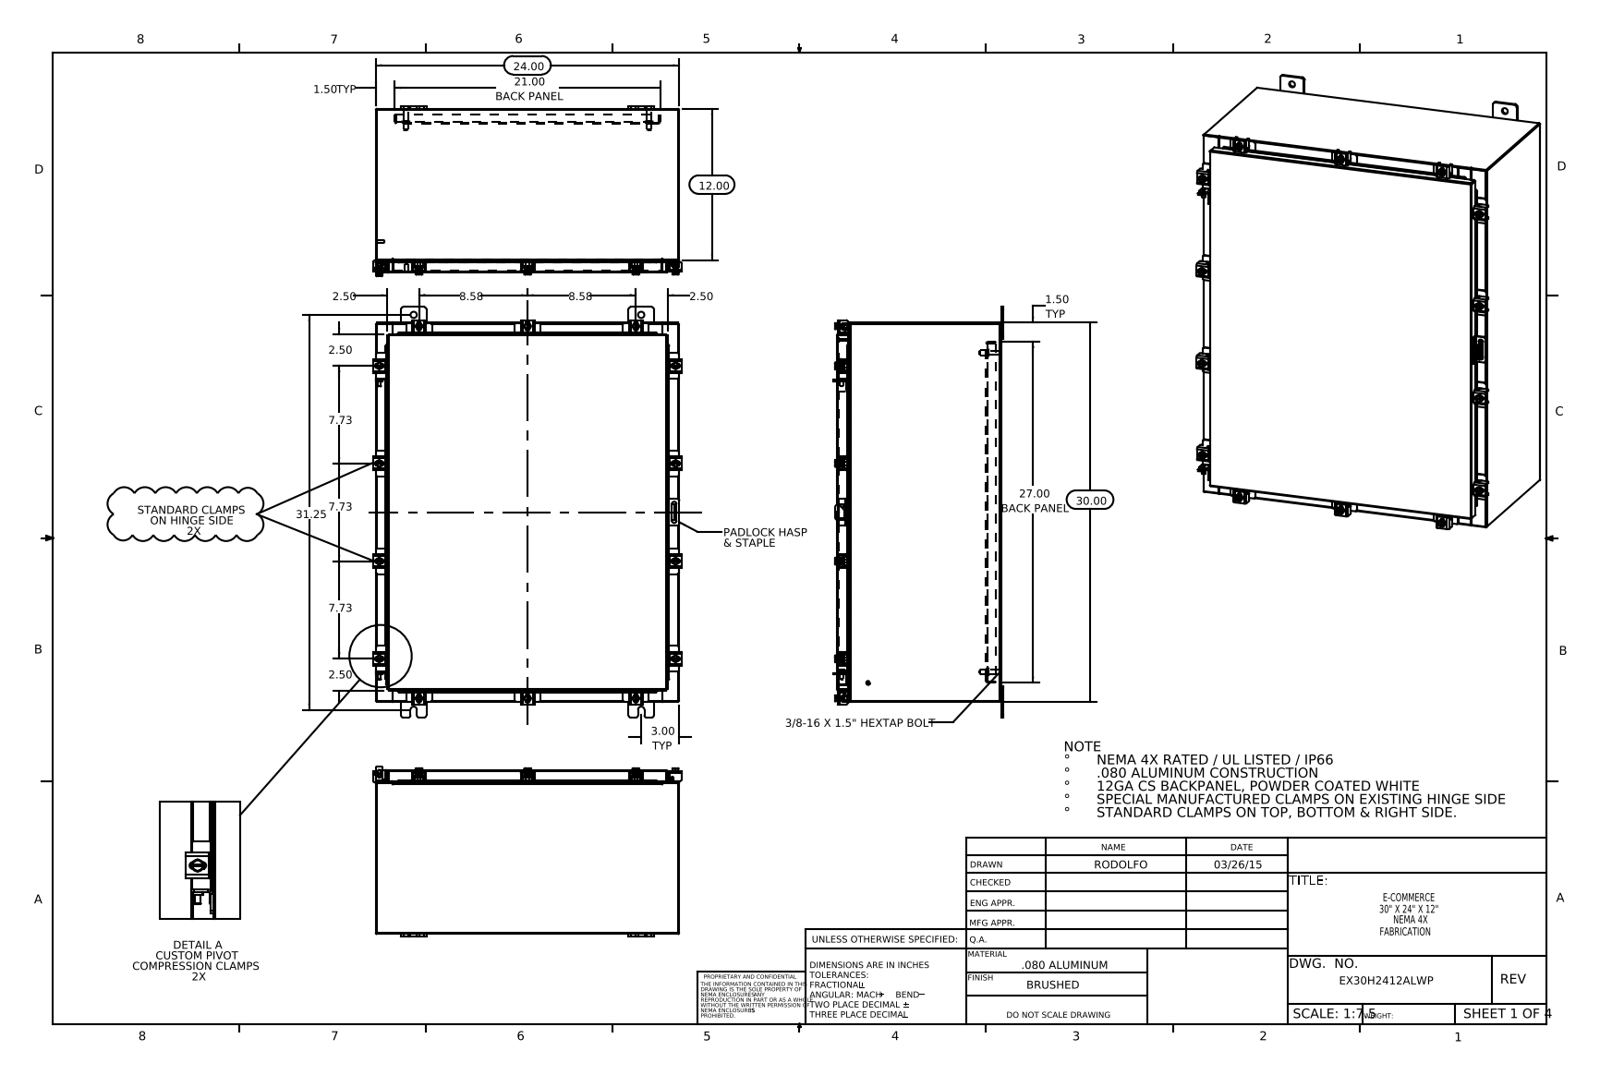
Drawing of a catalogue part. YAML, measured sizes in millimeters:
part_name: "22101002_RTP29; EX30H2412ALWP Backpanel; HW-CLN-NH-20330; EX30H2412ALWP Cover (+8 more)"
step_written_by: "SolidWorks 2014 (CONFIG_CONTROL_DESIGN)"
units: millimeters
bodies: {solids: 91, faces: 2272, planar: 1211, cylindrical: 885, other: 176}
overall_size: [825.5, 620.3, 341.7]
volume: 4862000
surface_area: 4796000
round_holes:
  - {diameter: 5.4, count: 14}
  - {diameter: 6.6, count: 14}
  - {diameter: 12.7, count: 8}
  - {diameter: 3.2, count: 1}
  - {diameter: 6.4, count: 1}
round_bosses_or_shafts:
  - {diameter: 12.7, count: 14}
  - {diameter: 6.4, count: 14}
  - {diameter: 10.1, count: 12}
  - {diameter: 15.9, count: 4}
  - {diameter: 9.5, count: 4}
  - {diameter: 8.4, count: 4}
  - {diameter: 8, count: 2}
  - {diameter: 6, count: 2}
partial_cylinders:
  - {radius: 1.5, count: 62}
  - {radius: 3.6, count: 28}
  - {radius: 0.3, count: 26}
  - {radius: 3, count: 26}
  - {radius: 4.8, count: 24}
  - {radius: 2.2, count: 22}
  - {radius: 2.3, count: 20}
  - {radius: 1.3, count: 19}
face_to_face_distances: [1.9, 327.7, 607.7, 329.6, 325.8, 2.6, 25.4, 760.1, 27.3, 300.4]
hole_center_spacings: [59.6, 112.8, 521.8, 595.7, 617.5, 673.3, 695.2, 820.1]
